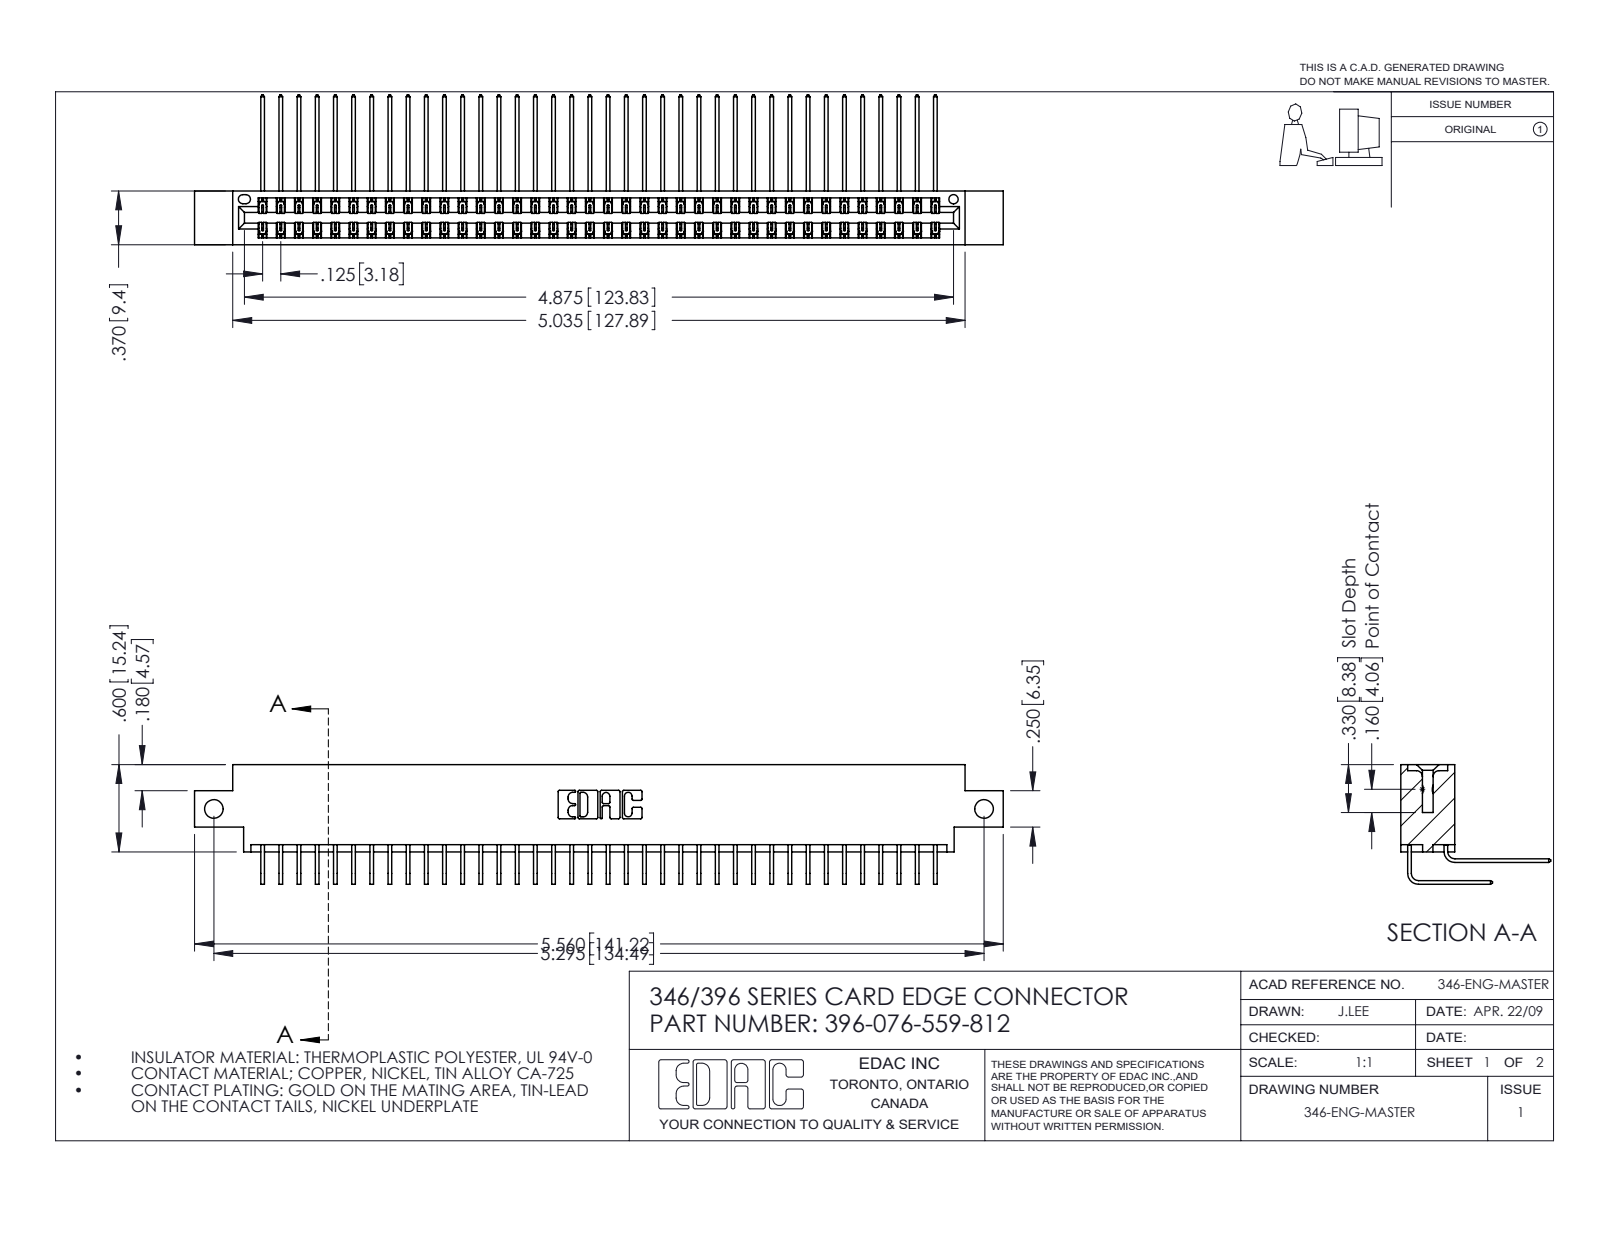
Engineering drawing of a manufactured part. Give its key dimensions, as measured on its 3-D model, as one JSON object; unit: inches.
{"part_name": "396-076-559-812; 345-292-001_558 559 Tail - 1; 346 Part_0.170 Offset - Side Mount; 345-292-001_559 Tail - 2", "step_written_by": "SolidWorks 2016 (CONFIG_CONTROL_DESIGN)", "units": "inches", "bodies": {"solids": 77, "faces": 4230, "planar": 2892, "cylindrical": 1338, "other": 0}, "overall_size": [5.56, 1.03, 0.823], "volume_in3": 0.85, "surface_area_in2": 32.92, "round_holes": [[0.128, 2], [0.064, 1]], "partial_cylinders_radius": [[0.006, 114], [0.01, 22], [0.007, 6], [0.031, 6], [0.026, 3], [0.014, 2], [0.022, 2], [0.024, 2]], "face_to_face_distances": [0.048, 0.322, 0.025, 0.37, 0.25, 0.072, 0.298, 0.275, 0.148, 0.222], "hole_center_spacings": [5.295]}
